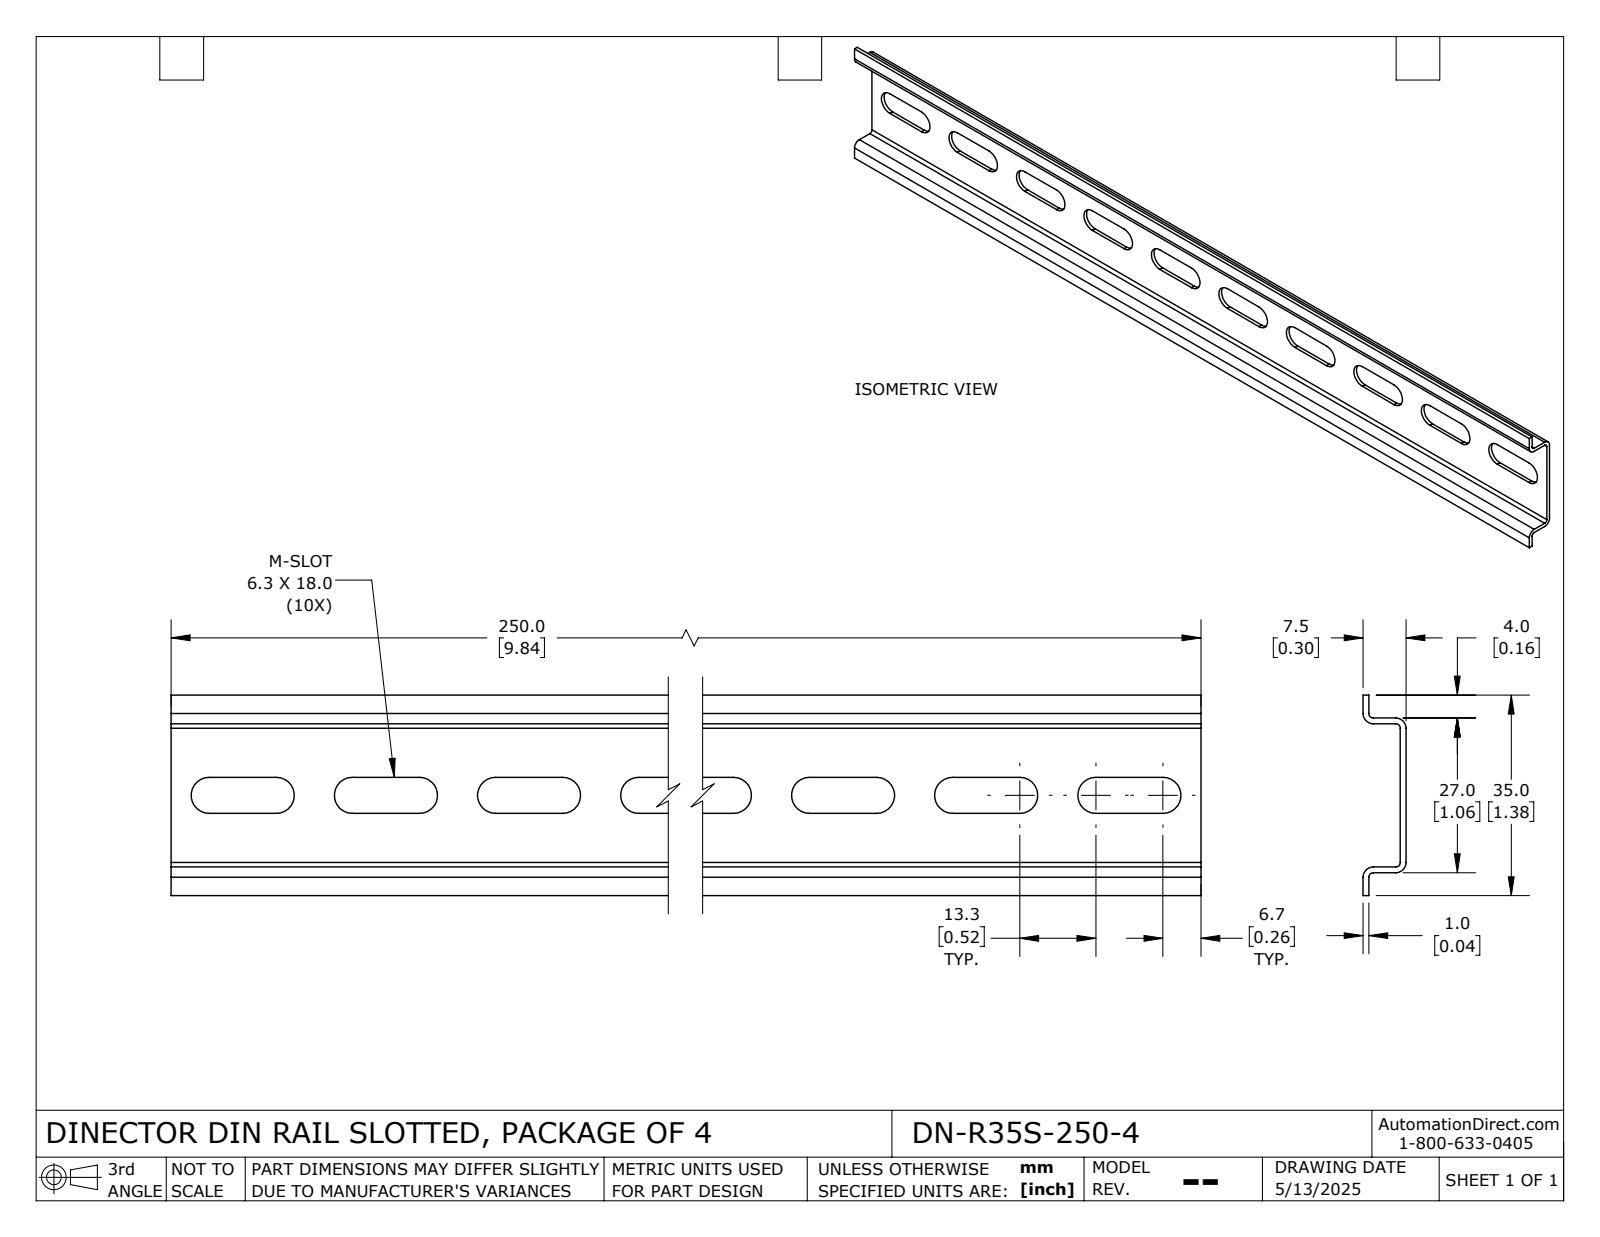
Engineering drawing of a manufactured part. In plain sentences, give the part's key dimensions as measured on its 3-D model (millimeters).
The part is named "DN-R35S-250-4_Default". Its 3-D file was written by "SolidWorks 2024 (CONFIG_CONTROL_DESIGN)". It is 1 solid with 62 faces: 34 planar, 28 cylindrical and 0 other. Overall it measures 250 by 35 by 7.5 millimeters. Its volume is 10 393 cubic millimeters and its surface area 21 810 square millimeters. Partial cylindrical surfaces (rounded edges, fillets, slot ends): 20 of radius 3.15, 4 of radius 0.8, 4 of radius 1.8. The main face-to-face distances are 1, 6.5, 26, 7.5, 5.5, 27, 25, 4, 5, 30.
